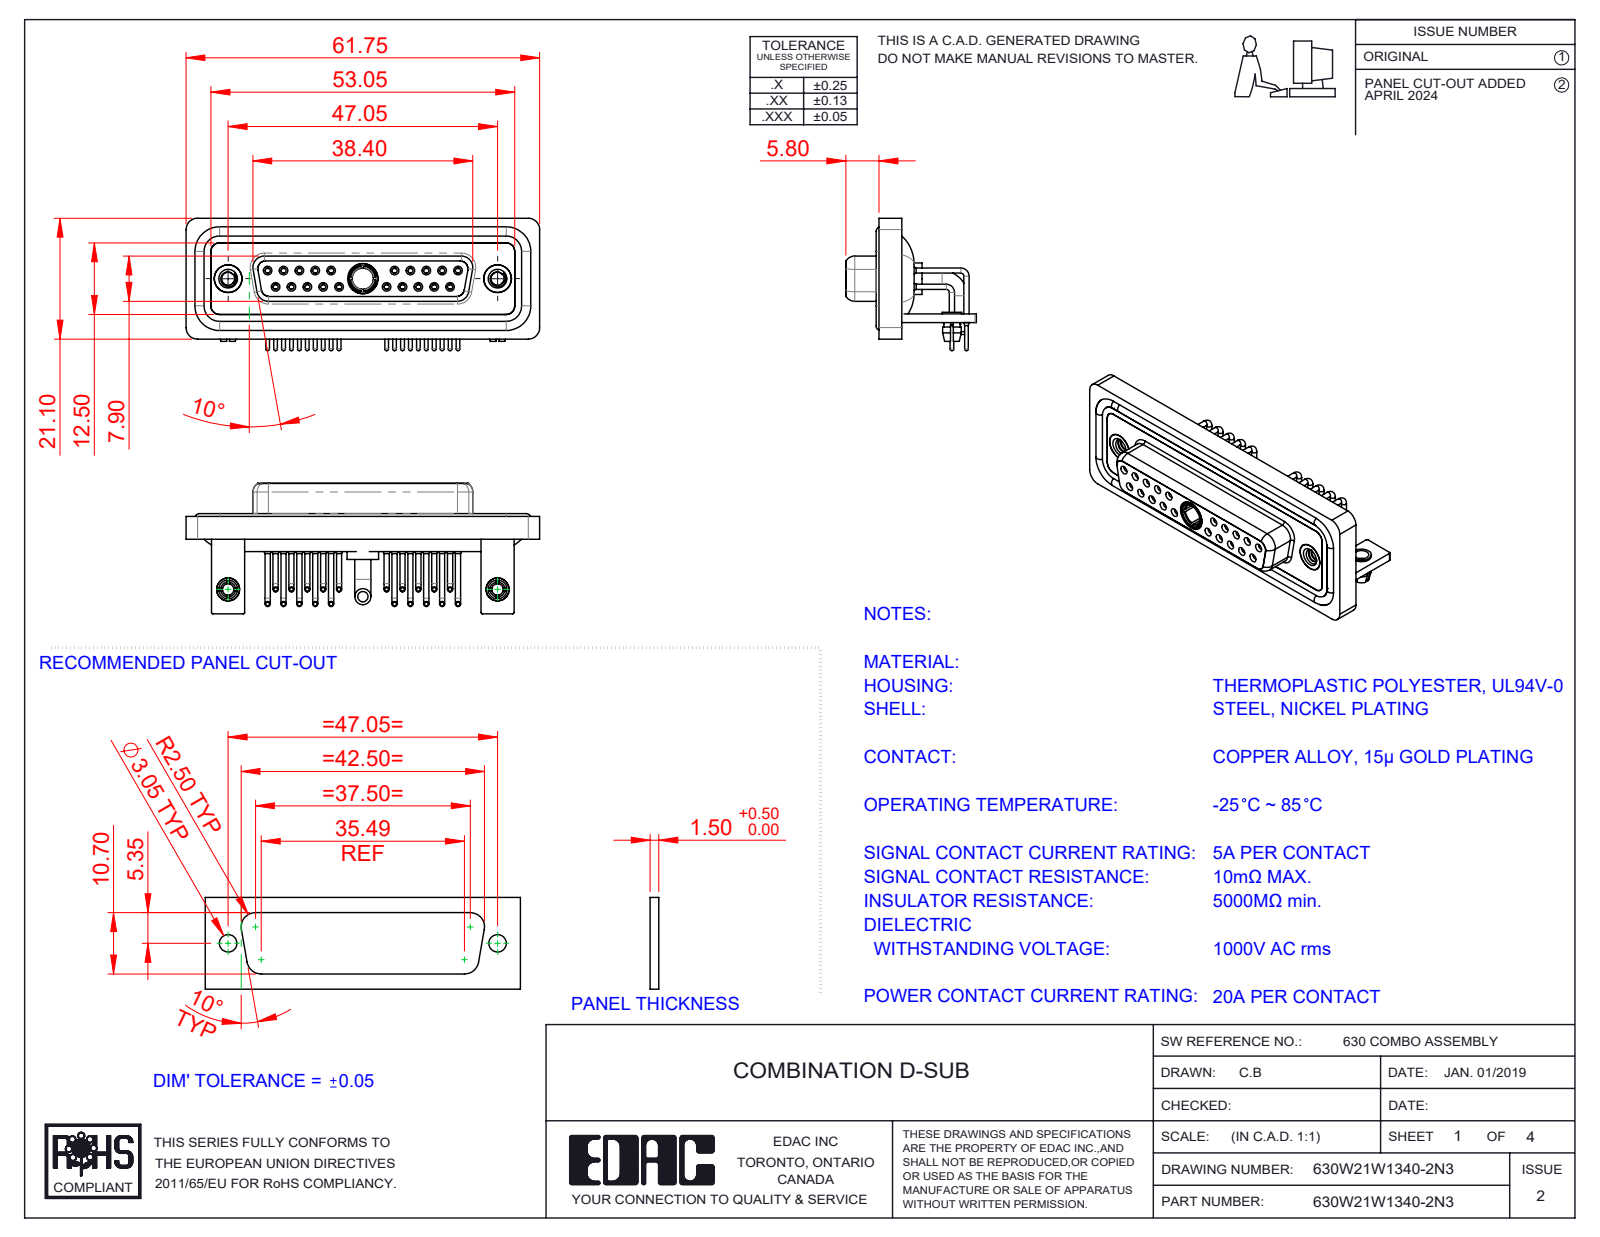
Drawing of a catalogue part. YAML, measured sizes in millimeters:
part_name: "630Combo Stabilizer Bracket_50 Contacts; 630Combo Housing_21W1; 630Combo Shell Rear_25 Contacts; 630Combo Threaded Rivet_2 (+7 more)"
step_written_by: "SolidWorks 2023 (CONFIG_CONTROL_DESIGN)"
units: millimeters
bodies: {solids: 33, faces: 1664, planar: 502, cylindrical: 729, other: 433}
overall_size: [61.75, 23.12, 22.8]
volume: 8908
surface_area: 15725
round_holes:
  - {diameter: 2, count: 22}
  - {diameter: 0.9, count: 20}
  - {diameter: 1.1, count: 20}
  - {diameter: 1.5, count: 20}
  - {diameter: 1.6, count: 10}
  - {diameter: 1.7, count: 10}
  - {diameter: 4.85, count: 3}
  - {diameter: 2.26, count: 2}
  - {diameter: 2.5, count: 2}
  - {diameter: 3.2, count: 2}
  - {diameter: 4, count: 2}
  - {diameter: 4.05, count: 2}
round_bosses_or_shafts:
  - {diameter: 0.9, count: 20}
  - {diameter: 0.65, count: 20}
  - {diameter: 1.6, count: 14}
  - {diameter: 4.95, count: 2}
  - {diameter: 4.8, count: 2}
  - {diameter: 4, count: 2}
  - {diameter: 3.4, count: 2}
  - {diameter: 3.3, count: 2}
partial_cylinders:
  - {radius: 2, count: 19}
  - {radius: 1.5, count: 18}
  - {radius: 0.25, count: 16}
  - {radius: 1.35, count: 8}
  - {radius: 1.6, count: 8}
  - {radius: 0.5, count: 5}
  - {radius: 0.6, count: 4}
  - {radius: 0.65, count: 4}
face_to_face_distances: [0.4, 1.8, 2.9, 3.7, 1.5, 4.1, 1.1, 1.4, 1.6, 2.5]
hole_center_spacings: [3.16, 2.77, 5.54, 8.31, 5.04, 19.39, 20.97, 22.16]
